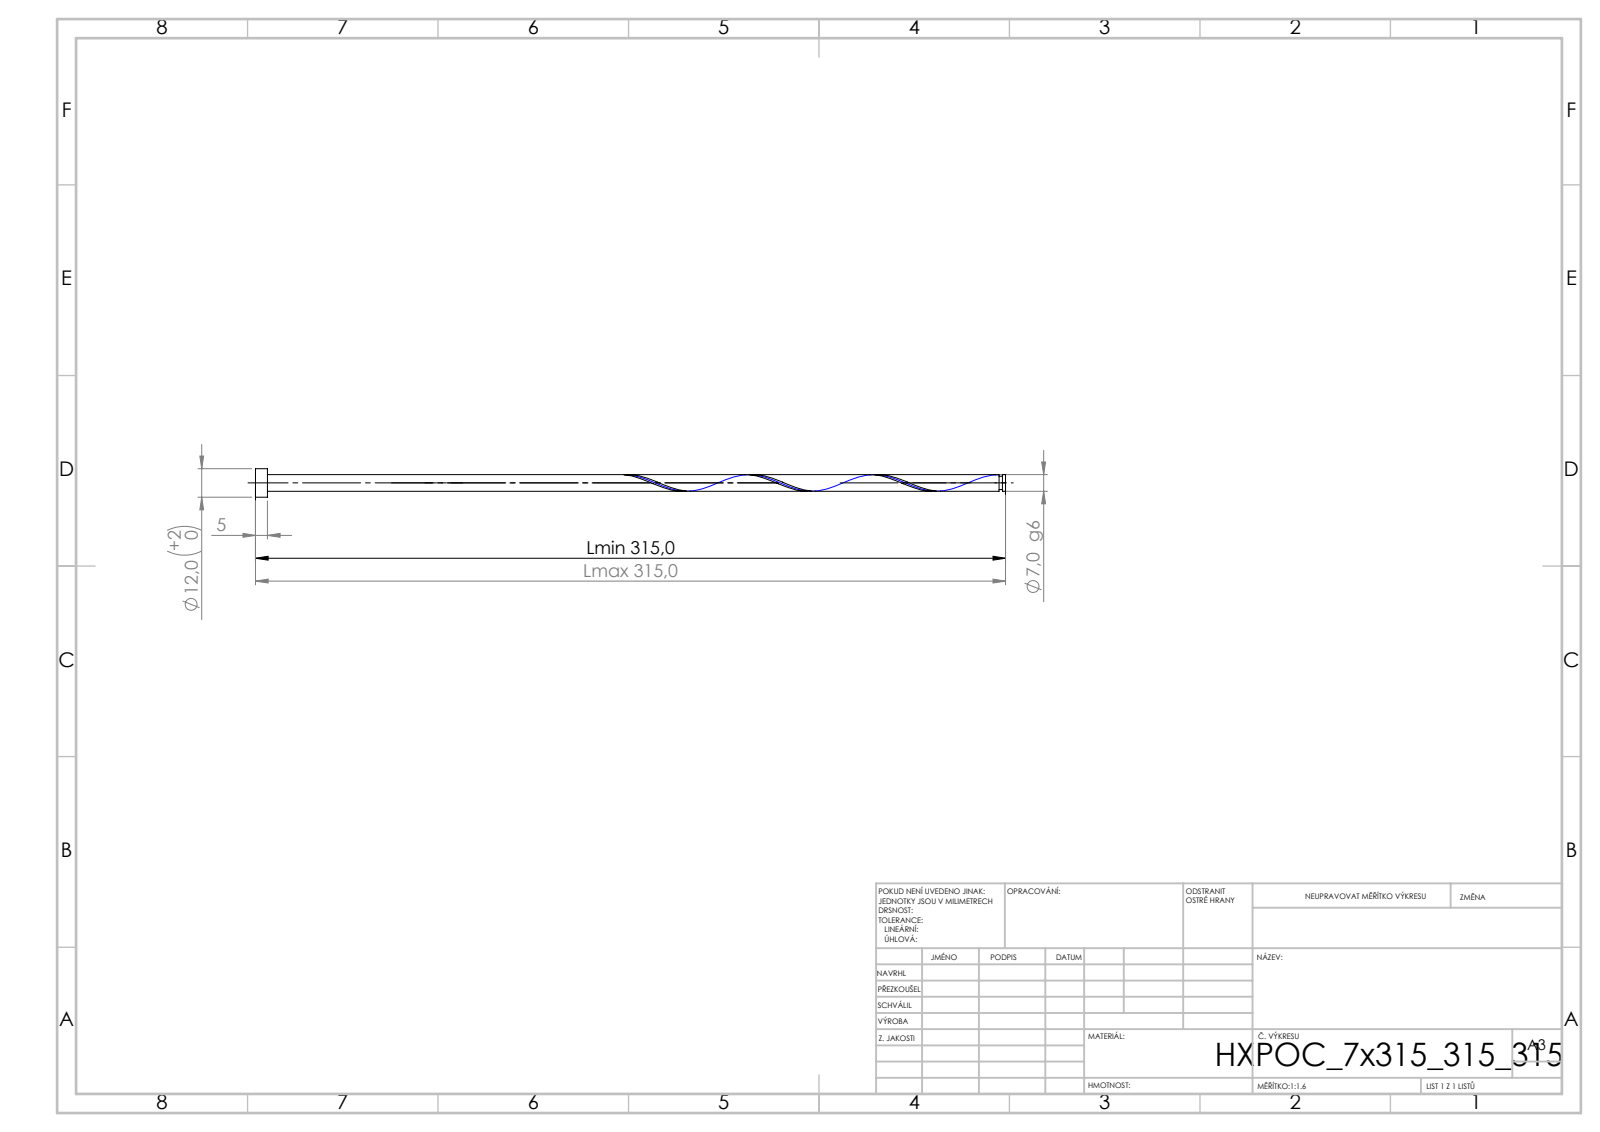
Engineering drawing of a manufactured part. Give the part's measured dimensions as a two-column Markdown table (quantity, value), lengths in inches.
| quantity | value |
| --- | --- |
| STEP written by | SolidWorks 2019 (CONFIG_CONTROL_DESIGN) |
| units | inches |
| bodies | 1 solid, 21 faces (6 planar, 14 cylindrical, 1 other) |
| overall size | 12.402 × 0.472 × 0.472 |
| volume | 0.754 in³ |
| surface area | 11.42 in² |
| round bosses / shafts (diameter × count) | 0.472 × 1, 0.276 × 1, 0.22 × 1 |
| main face-to-face distances | 0.197, 12.402, 12.205, 12.35, 12.153, 0.052, 12.295, 12.098, 0.055, 0.107 |
